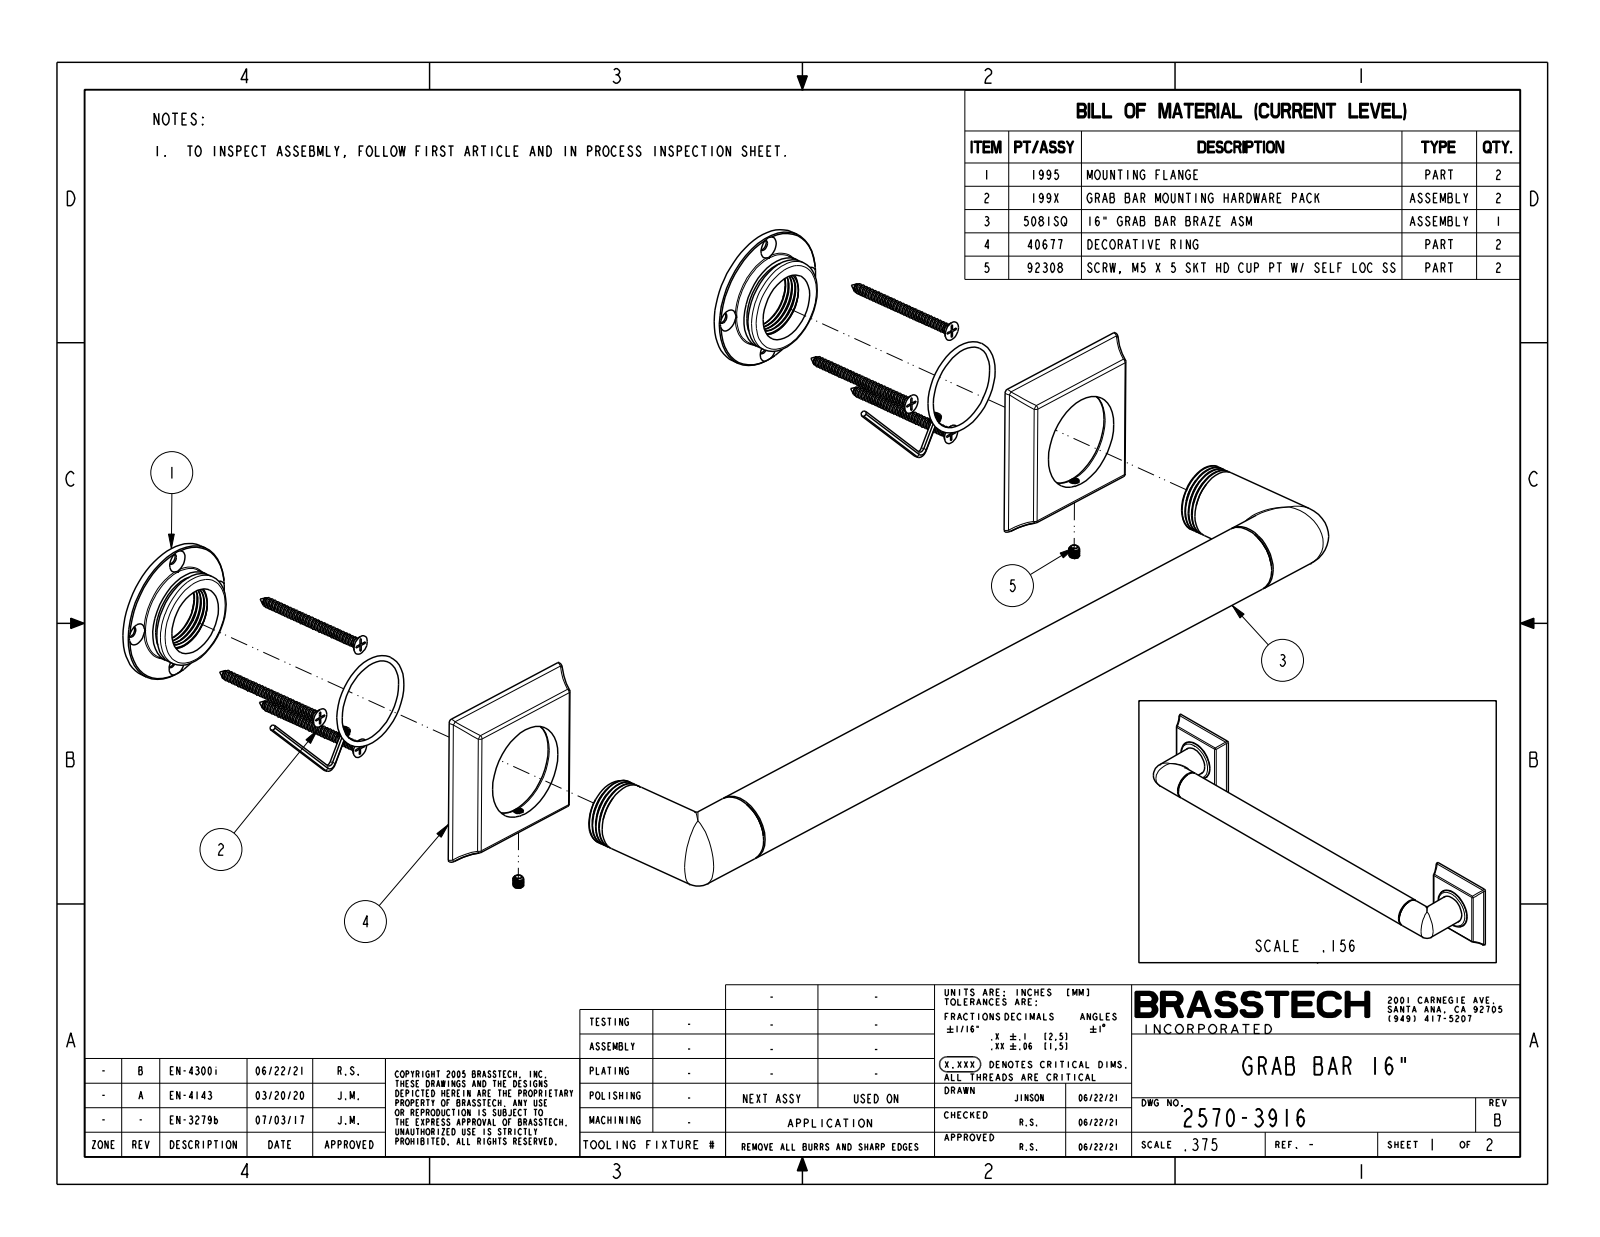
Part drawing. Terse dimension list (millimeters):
name: 2570-3916
written by: CREO PARAMETRIC BY PTC INC, 2018400 (CONFIG_CONTROL_DESIGN)
unit: mm
bodies: 1 solid, 88 faces (6 planar, 38 cylindrical, 44 other)
size: 482.6 × 76.2 × 70
volume: 514 600 mm³; area: 74 390 mm²
bosses: 3× ⌀31.8, 2× ⌀44.5
rounds: 6× R1.5, 6× R3.2, 6× R34.3
face distances: 13.3, 15.2, 1.9
